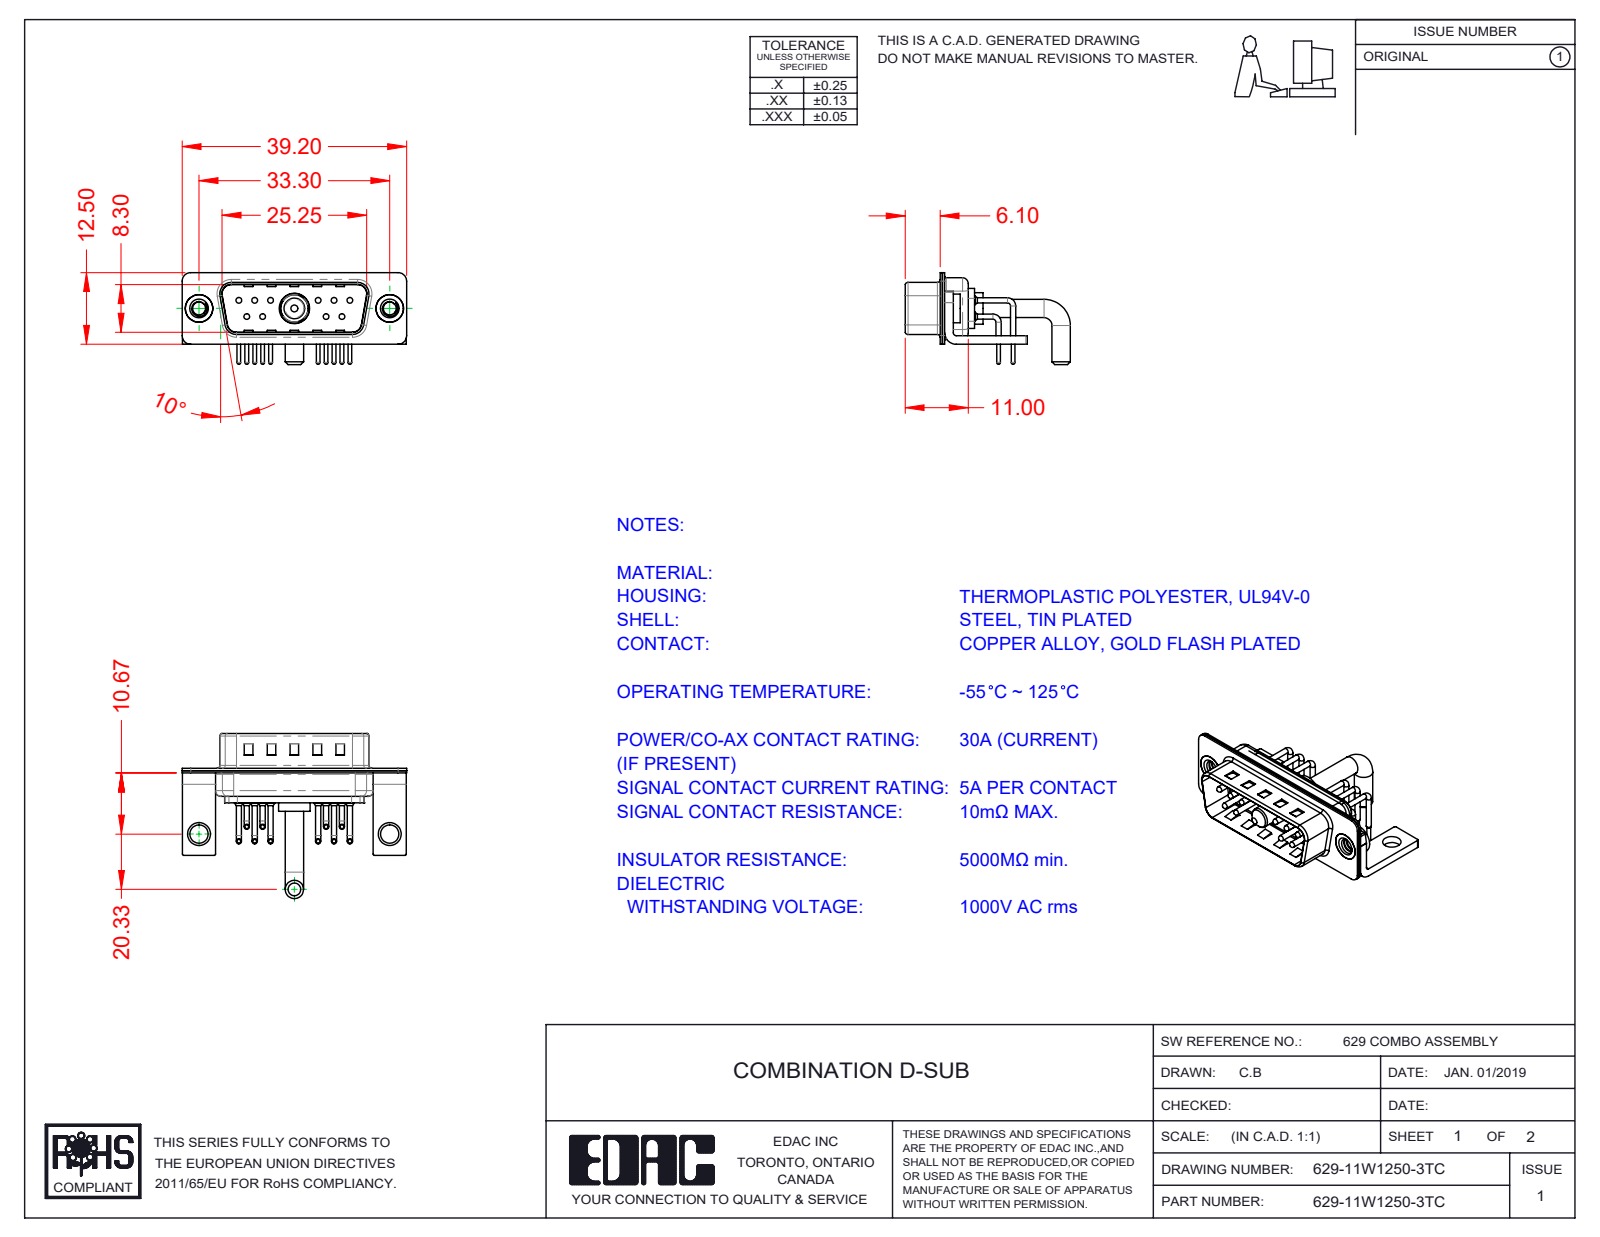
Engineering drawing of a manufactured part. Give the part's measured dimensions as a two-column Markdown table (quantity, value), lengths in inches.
| quantity | value |
| --- | --- |
| part name | 629Combo Stabilizer Bracket; 629Combo Housing_11W1; 629Combo Contact Row 2; 629Combo Contact Row 1 (+5 more) |
| STEP written by | SolidWorks 2020 (CONFIG_CONTROL_DESIGN) |
| units | inches |
| bodies | 19 solids, 1544 faces (818 planar, 542 cylindrical, 184 other) |
| overall size | 1.543 × 1.135 × 0.632 |
| volume | 0.15 in³ |
| surface area | 9.247 in² |
| round holes (diameter × count) | 0.03 × 10, 0.063 × 10, 0.079 × 10, 0.089 × 2, 0.126 × 2, 0.157 × 2, 0.189 × 2, 0.191 × 1, 0.209 × 1 |
| round bosses / shafts (diameter × count) | 0.035 × 20, 0.059 × 10, 0.039 × 10, 0.026 × 10, 0.197 × 2, 0.193 × 2, 0.126 × 2, 0.217 × 1 |
| partial cylindrical surfaces (radius × count) | 0.01 × 16, 0.059 × 16, 0.079 × 13, 0.04 × 10, 0.02 × 9, 0.063 × 8, 0.039 × 7, 0.024 × 4 |
| main face-to-face distances | 0.016, 0.031, 0.059, 0.374, 0.358, 0.024, 0.343, 0.39, 0.047, 0.205 |
| hole center spacings | 0.124, 0.109, 0.545, 0.436, 0.654, 0.198, 0.198, 0.218 |
